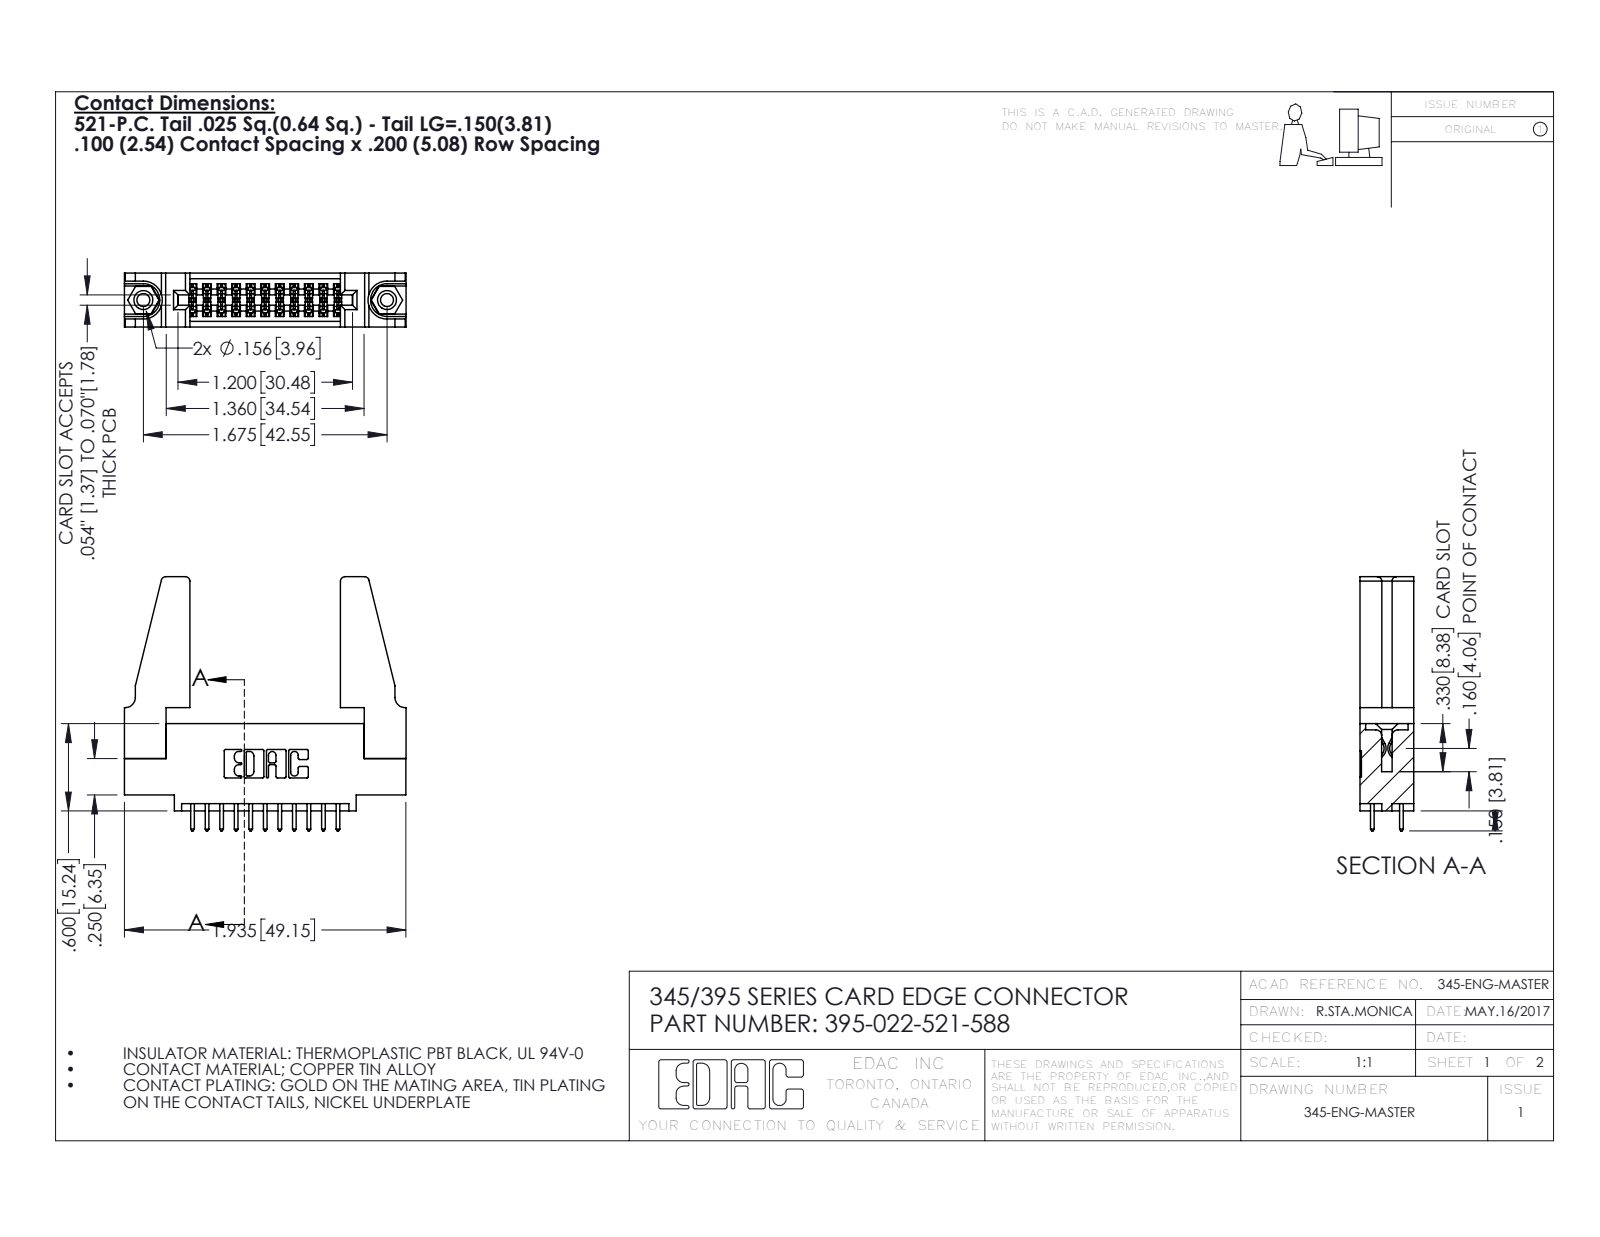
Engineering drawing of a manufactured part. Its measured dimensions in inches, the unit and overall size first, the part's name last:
Units: inches
Overall size (bounding box): 1.936 × 1.747 × 0.37
Round holes (diameter × count): ⌀0.089 ×2, ⌀0.125 ×2, ⌀0.156 ×2, ⌀0.064 ×1
Round bosses / shafts (diameter × count): ⌀0.155 ×2
Partial cylindrical surfaces — rounded edges, fillets, slot ends (radius × count): R0.006 ×33, R0.01 ×22, R0.01 ×22, R0.03 ×8, R0.007 ×6, R0.031 ×6, R0.026 ×3, R0.014 ×2
Main face-to-face distances: 0.37, 0.072, 0.298, 0.2, 0.098, 0.272, 0.025, 0.225, 0.148, 0.15
Hole centre spacings: 0.27, 1.443, 1.675
Volume: 0.467 in³ · Surface area: 14.06 in²
Bodies: 27 solids, 1354 faces (882 planar, 456 cylindrical, 16 other)
Part name (STEP PRODUCT): 345 Part_0.110 Offset - 0.156 Dia-TH; 345-250-001_345-250-001-102; 395-022-521-588; 345-220-078_345-220-088 (+1 more)
STEP written by: SolidWorks 2016 (CONFIG_CONTROL_DESIGN)
